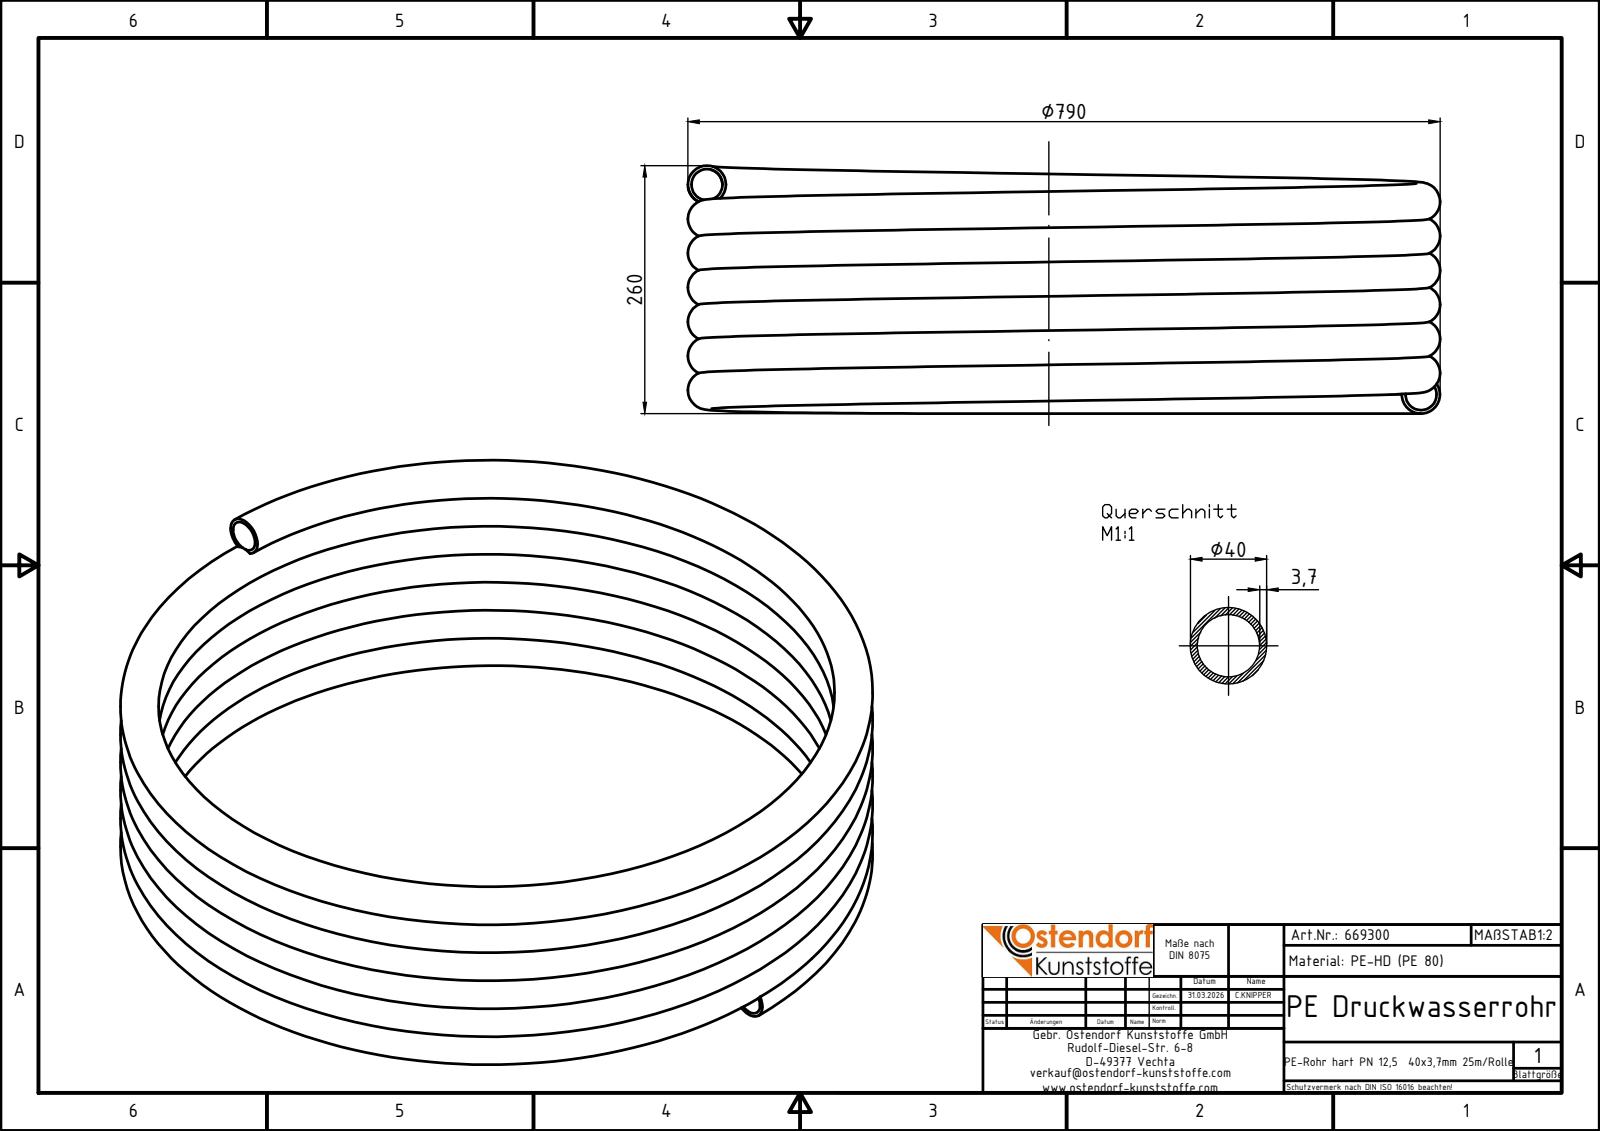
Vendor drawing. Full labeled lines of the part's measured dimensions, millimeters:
Part name (STEP PRODUCT): 669300z
STEP written by: Autodesk Inventor 2024 (AUTOMOTIVE_DESIGN)
Units: millimetres
Bodies: 1 solid, 7 faces (3 planar, 0 cylindrical, 4 other)
Overall size (bounding box): 790.01 × 790 × 260.03
Volume: 5 827 000 mm³ · Surface area: 2 964 000 mm²
